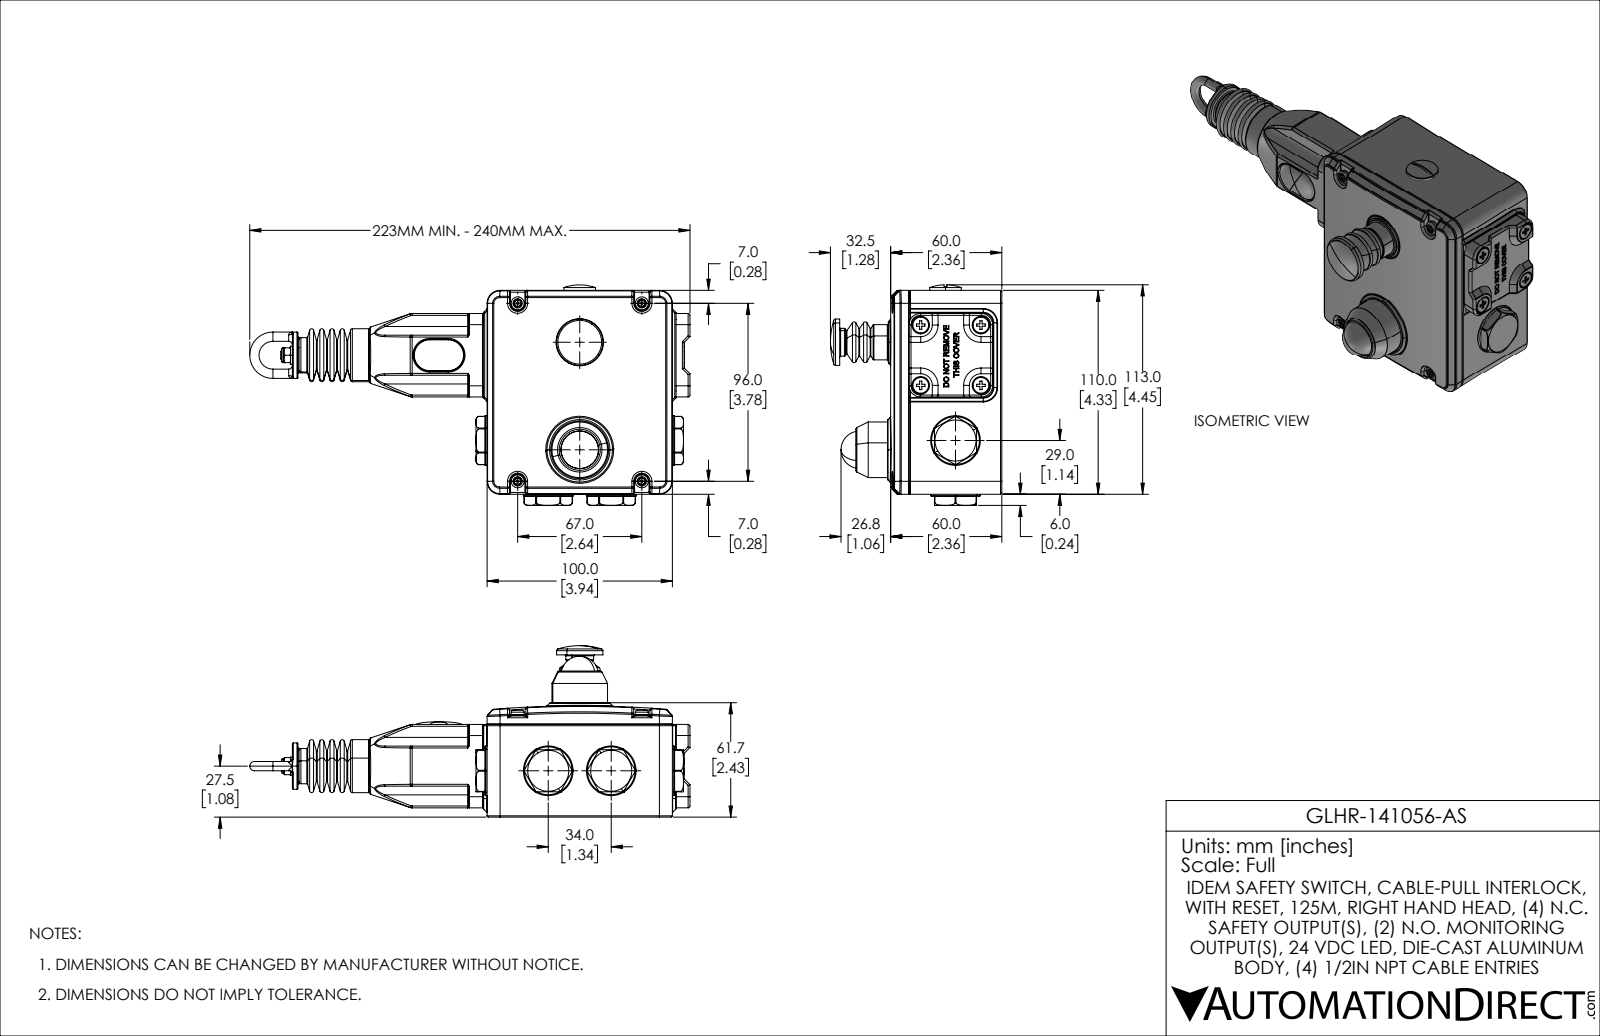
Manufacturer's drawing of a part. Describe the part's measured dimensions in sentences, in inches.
The part is named "GLHR-141056-AS". Its 3-D file was written by "SolidWorks 2021 (AUTOMOTIVE_DESIGN)". It is 41 solids with 4536 faces: 1445 planar, 1449 cylindrical and 1642 other. Overall it measures 9.354 by 4.685 by 3.642 inches. Its volume is 18.31 cubic inches and its surface area 285.5 square inches. Round holes: 10 of diameter 0.197, 9 of diameter 0.209, 7 of diameter 0.374, 5 of diameter 0.354, 4 of diameter 0.13, 4 of diameter 0.157, 4 of diameter 0.189, 4 of diameter 0.213, 4 of diameter 0.228, 3 of diameter 0.067, 3 of diameter 0.102, 3 of diameter 0.118. Round bosses or shafts: 7 of diameter 0.335, 7 of diameter 0.236, 7 of diameter 0.173, 6 of diameter 0.197, 5 of diameter 0.276, 4 of diameter 0.138, 4 of diameter 0.051, 3 of diameter 1.055. Partial cylindrical surfaces (rounded edges, fillets, slot ends): 241 of radius 0.02, 158 of radius 0.039, 76 of radius 0.008, 72 of radius 0.028, 26 of radius 0.012, 14 of radius 0.006, 12 of radius 0.236, 10 of radius 0.004. The main face-to-face distances are 0.138, 2.157, 0.114, 2.043, 4.331, 0.055, 0.079, 0.157, 4.016, 3.878. The hole center spacings are 1.28, 1.281, 0.228, 0.374, 0.905, 1.891, 1.913, 3.012.
